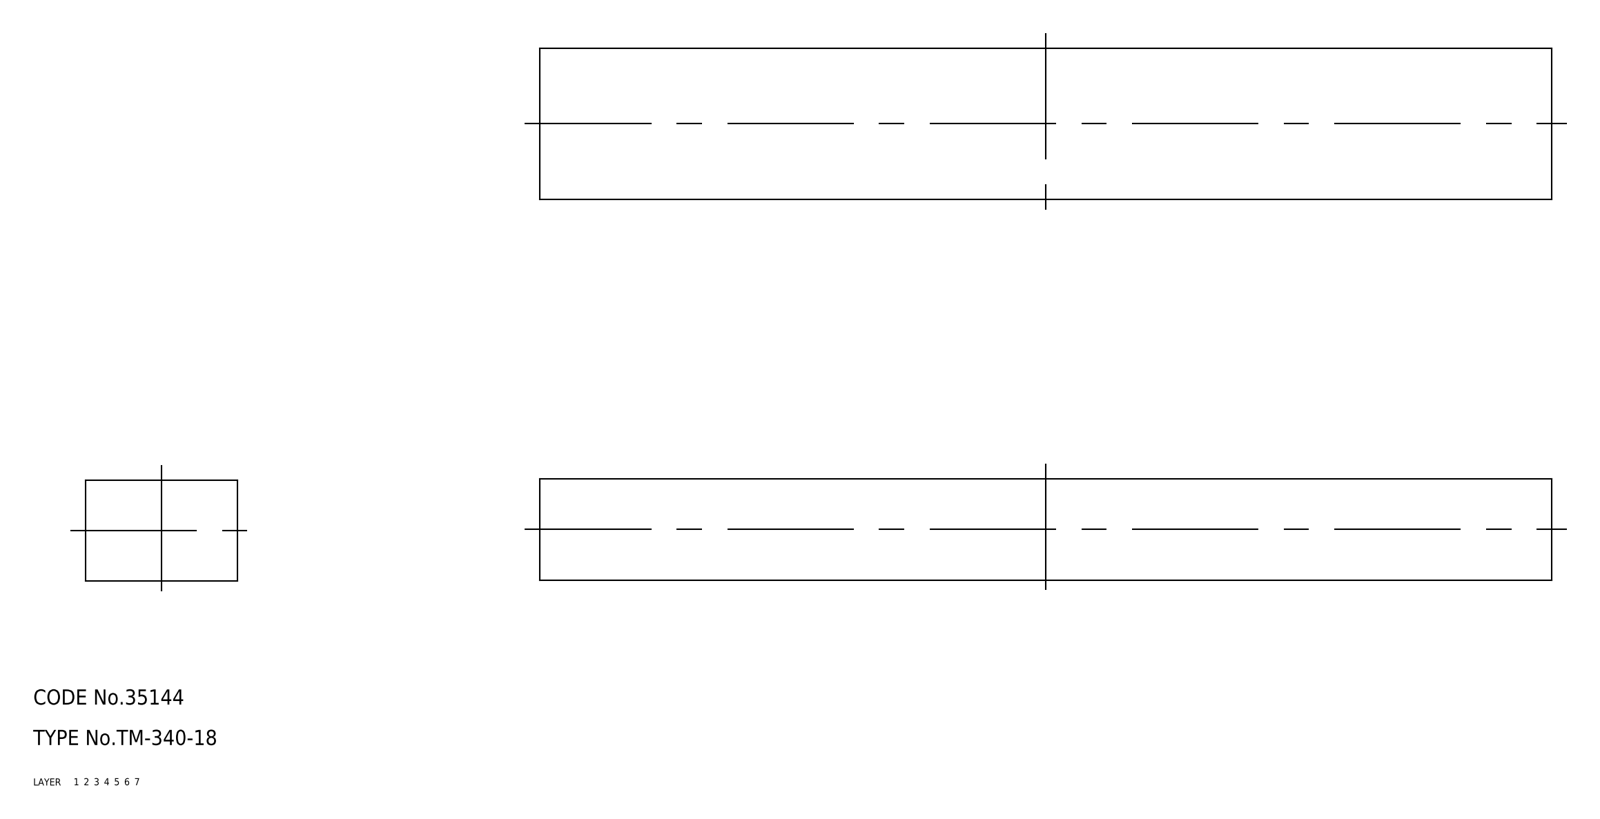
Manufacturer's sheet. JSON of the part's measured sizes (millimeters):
{"part_name": "TM_340_18; rubber foam", "step_written_by": "SolidWorks 2015 (AUTOMOTIVE_DESIGN)", "units": "millimeters", "bodies": {"solids": 1, "faces": 6, "planar": 6, "cylindrical": 0, "other": 0}, "overall_size": [200, 30, 20], "volume_mm3": 120000, "surface_area_mm2": 21200, "face_to_face_distances": [20, 30, 200]}
